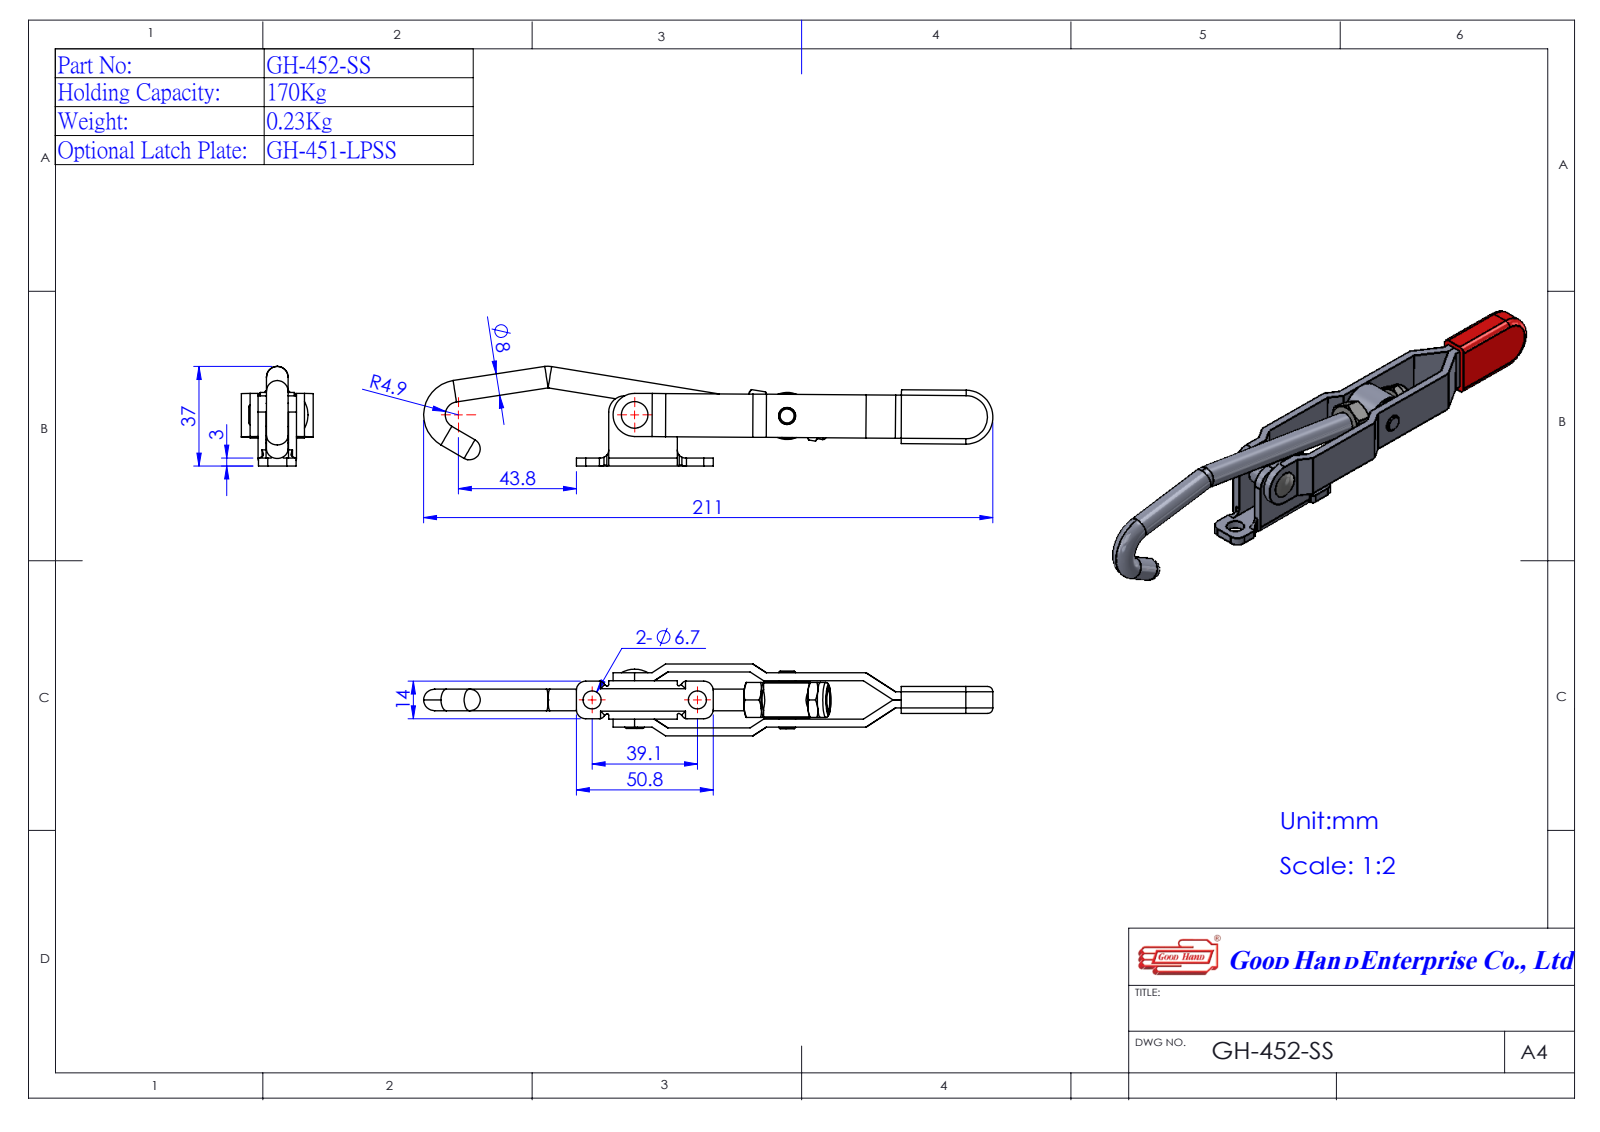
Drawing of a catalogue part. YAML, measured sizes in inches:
part_name: "Group2^GH-452(簡化); Group3^GH-452(簡化); GH-452-SS(簡化); 445144-1^GH-452(簡化) (+1 more)"
step_written_by: "SolidWorks 2016 (AUTOMOTIVE_DESIGN)"
units: inches
bodies: {solids: 6, faces: 201, planar: 81, cylindrical: 74, other: 46}
overall_size: [8.348, 1.437, 1.052]
volume: 2.141
surface_area: 35.03
round_holes:
  - {diameter: 0.315, count: 3}
  - {diameter: 0.264, count: 2}
  - {diameter: 0.268, count: 2}
  - {diameter: 0.197, count: 1}
  - {diameter: 0.244, count: 1}
  - {diameter: 0.371, count: 1}
round_bosses_or_shafts:
  - {diameter: 0.315, count: 3}
  - {diameter: 0.689, count: 1}
  - {diameter: 0.512, count: 1}
  - {diameter: 0.374, count: 1}
partial_cylinders:
  - {radius: 0.079, count: 5}
  - {radius: 0.02, count: 4}
  - {radius: 0.118, count: 4}
  - {radius: 0.138, count: 4}
  - {radius: 0.082, count: 2}
  - {radius: 0.087, count: 1}
  - {radius: 0.098, count: 1}
  - {radius: 0.236, count: 1}
face_to_face_distances: [0.117, 0.128, 0.807, 0.118, 0.68, 0.563, 0.201, 0.595, 0.085, 0.478]
hole_center_spacings: [1.539, 2.228]
